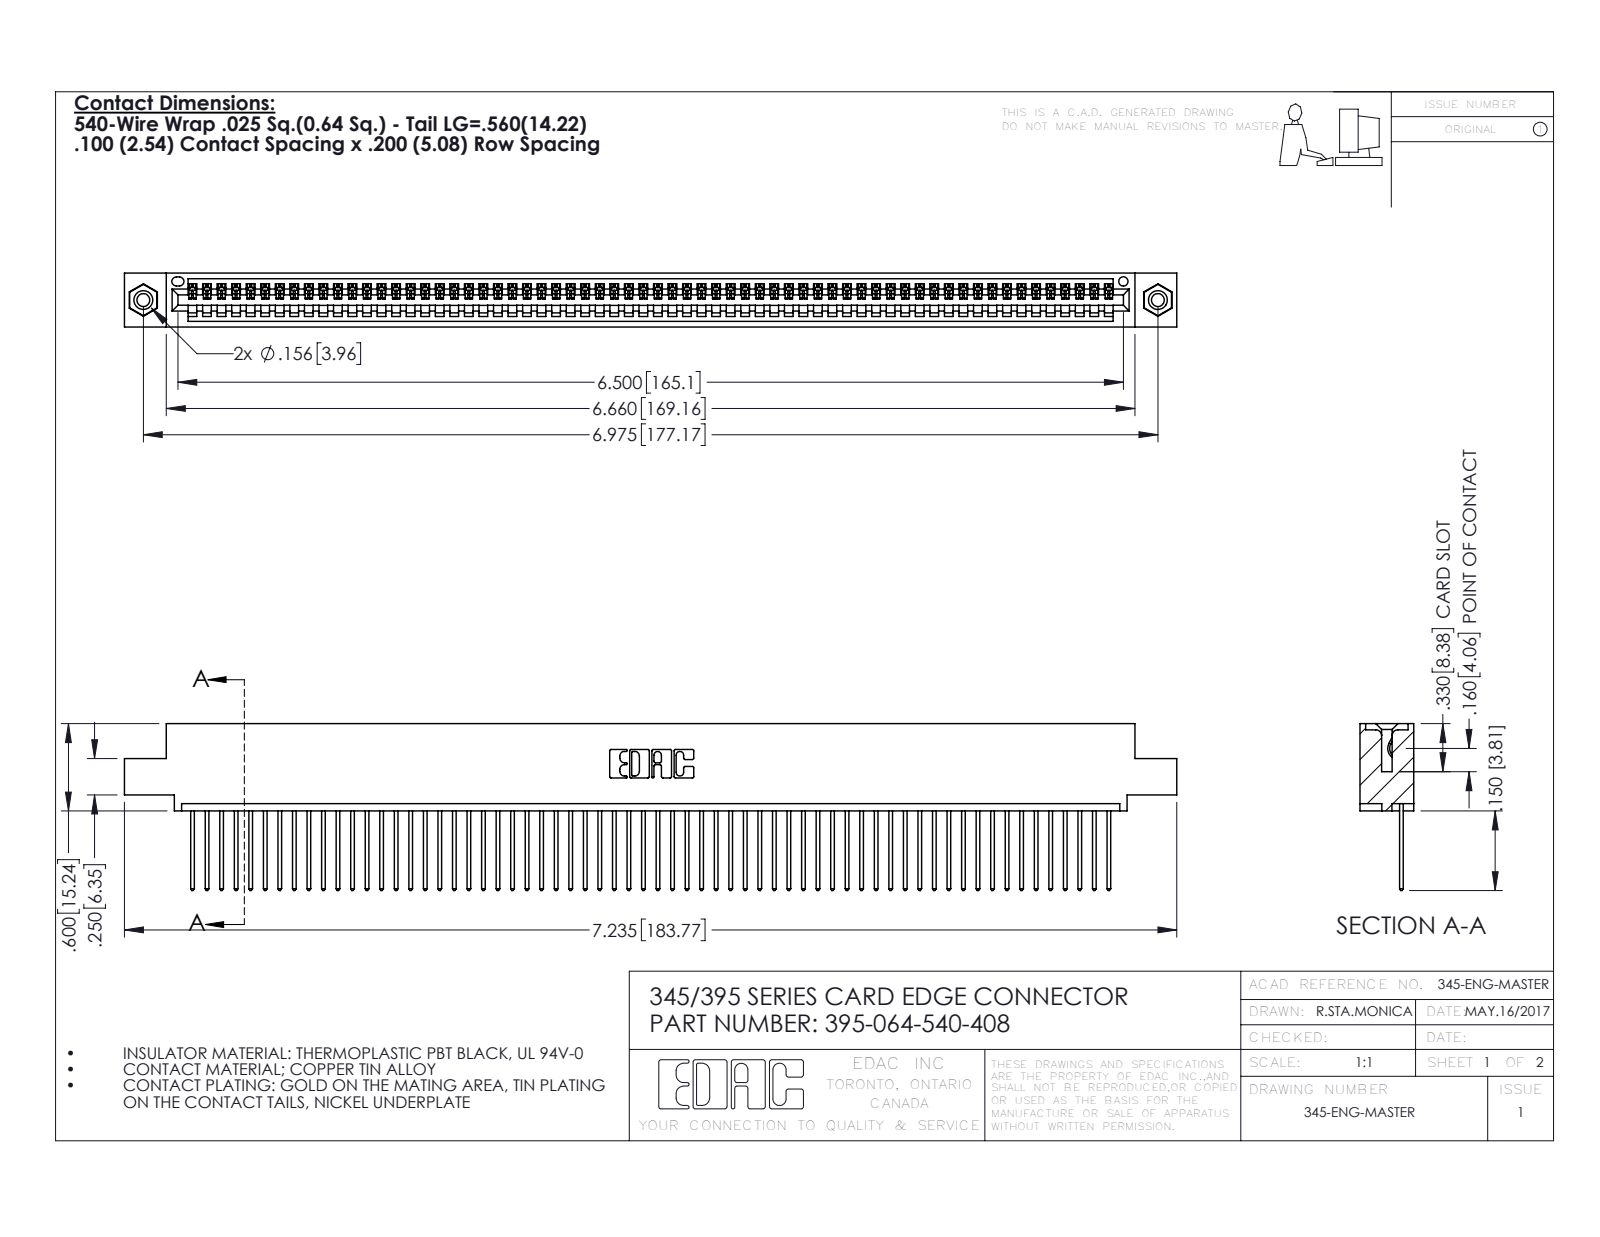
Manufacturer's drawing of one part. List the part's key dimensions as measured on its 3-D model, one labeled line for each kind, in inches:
Part name (STEP PRODUCT): 345-250-001_345-250-003-102; 345-292-001_345-293-140; 345 Part_0.110 Offset - 0.156 Dia-TI; 395-064-540-408
STEP written by: SolidWorks 2016 (CONFIG_CONTROL_DESIGN)
Units: inches
Bodies: 67 solids, 3902 faces (2676 planar, 1210 cylindrical, 16 other)
Overall size (bounding box): 7.235 × 1.147 × 0.37
Volume: 1.077 in³ · Surface area: 37.92 in²
Round holes (diameter × count): ⌀0.089 ×2, ⌀0.125 ×2, ⌀0.156 ×2, ⌀0.064 ×1
Round bosses / shafts (diameter × count): ⌀0.155 ×2
Partial cylindrical surfaces — rounded edges, fillets, slot ends (radius × count): R0.006 ×128, R0.01 ×128, R0.01 ×22, R0.007 ×6, R0.031 ×6, R0.026 ×3, R0.031 ×2, R0.04 ×2
Main face-to-face distances: 0.072, 0.298, 0.37, 0.098, 0.272, 0.025, 0.2, 0.225, 0.149, 0.072
Hole centre spacings: 0.27, 6.739, 6.975
